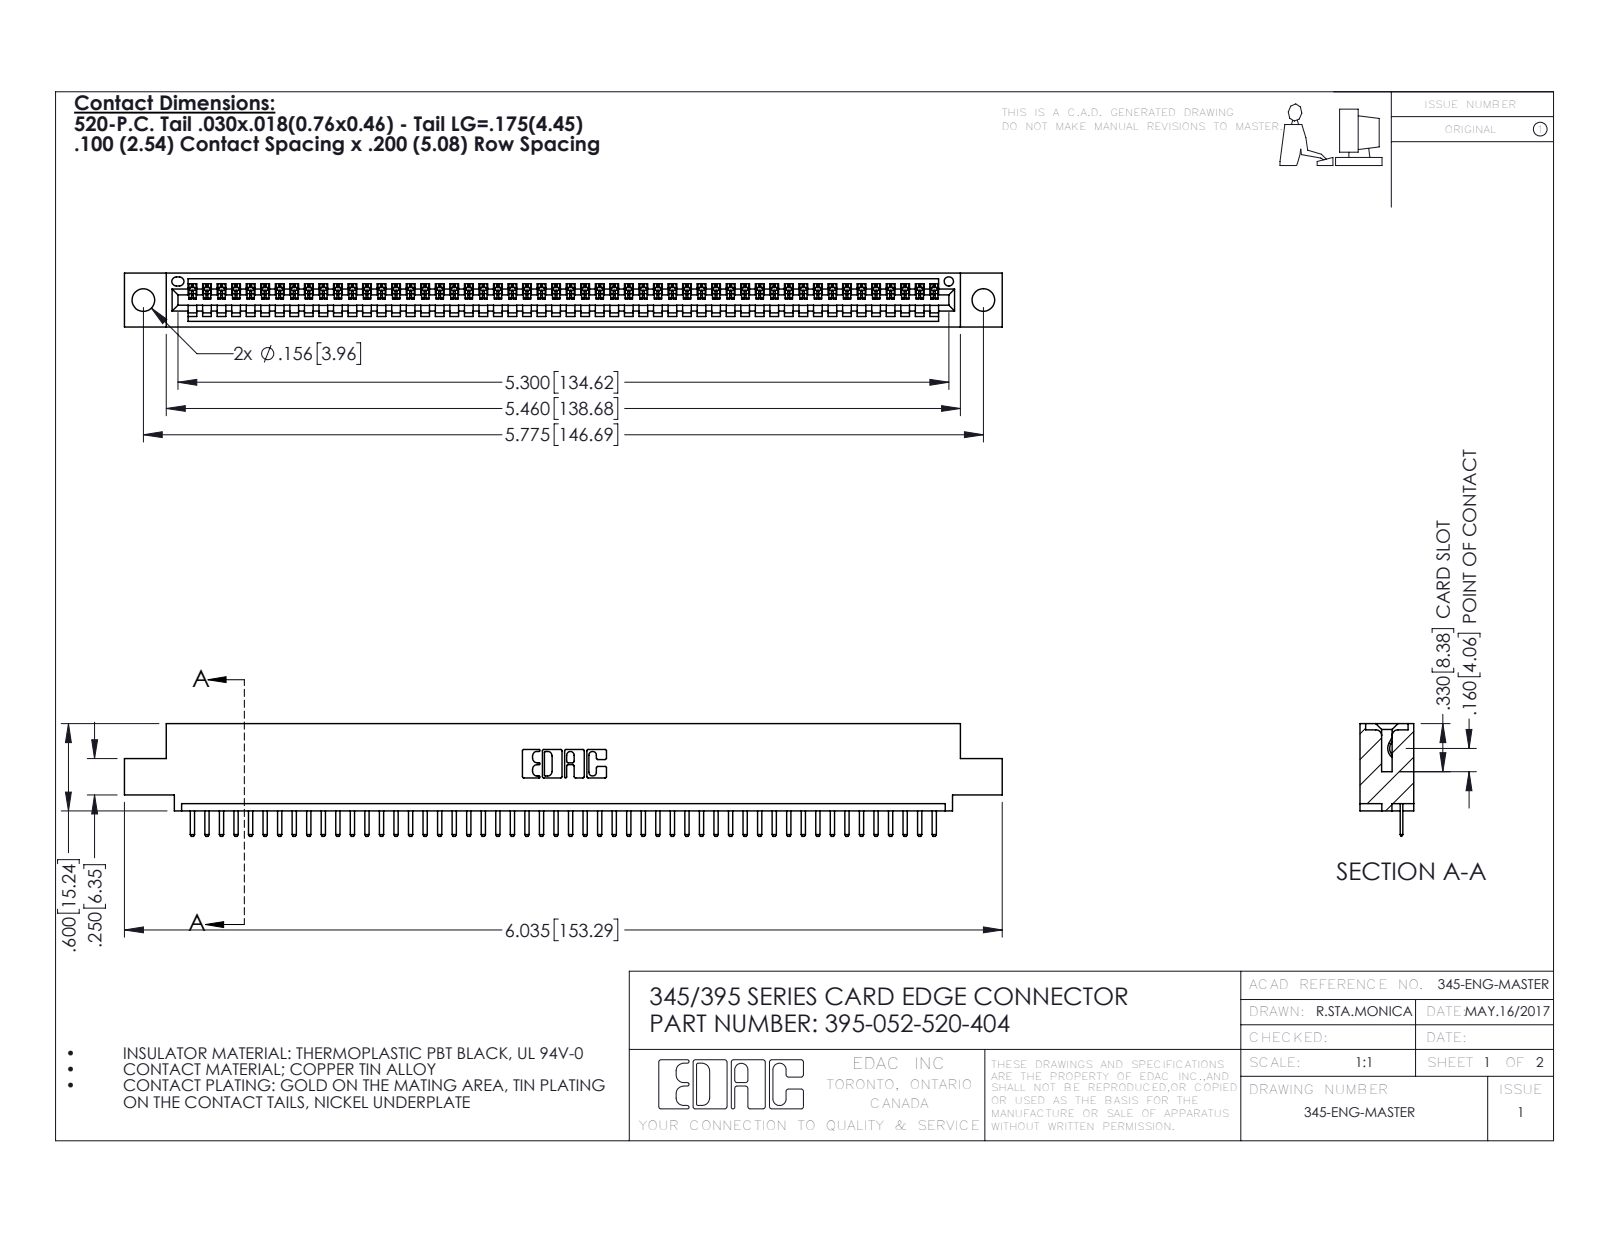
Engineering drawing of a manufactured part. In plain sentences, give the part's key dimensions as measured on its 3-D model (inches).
The part is named "395-052-520-404; 345-292-001_345-293-120; 345 Part_0.110 Offset - 0.156 Dia-TH". Its 3-D file was written by "SolidWorks 2016 (CONFIG_CONTROL_DESIGN)". It is 53 solids with 3354 faces: 2268 planar, 1086 cylindrical and 0 other. Overall it measures 6.035 by 0.775 by 0.37 inches. Its volume is 0.875 cubic inches and its surface area 28.8 square inches. Round holes: 2 of diameter 0.156, 1 of diameter 0.064. Partial cylindrical surfaces (rounded edges, fillets, slot ends): 106 of radius 0.01, 104 of radius 0.006, 22 of radius 0.01, 6 of radius 0.007, 6 of radius 0.031, 3 of radius 0.026, 2 of radius 0.031, 2 of radius 0.04. The main face-to-face distances are 0.298, 0.072, 0.37, 0.2, 0.098, 0.272, 0.025, 0.225, 0.072, 0.149. The hole center spacings are 0.27, 5.539, 5.775.
